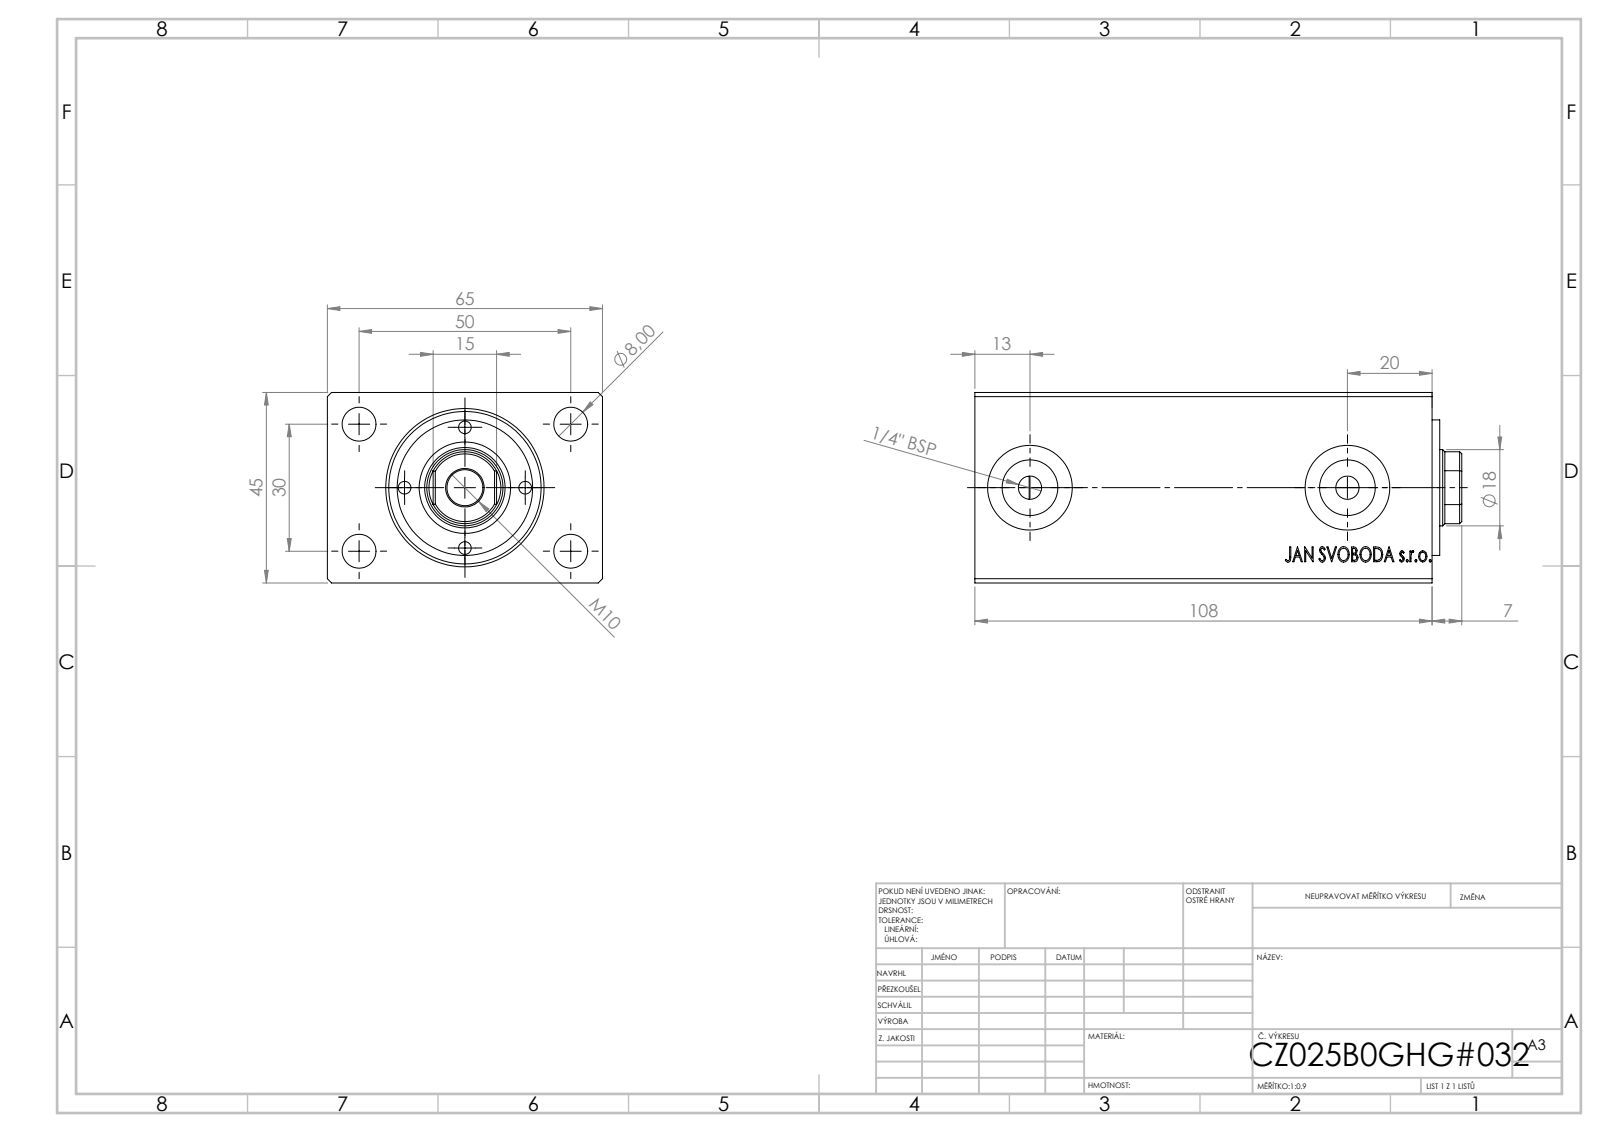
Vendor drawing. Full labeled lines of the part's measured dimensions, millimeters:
Part name (STEP PRODUCT): V500CZ; V500CZ_B_VC
STEP written by: SolidWorks 2019 (CONFIG_CONTROL_DESIGN)
Units: millimetres
Bodies: 3 solids, 873 faces (399 planar, 58 cylindrical, 416 other)
Overall size (bounding box): 115 × 65 × 45
Volume: 293 860 mm³ · Surface area: 54 520 mm²
Round holes (diameter × count): ⌀3 ×4, ⌀8 ×4, ⌀5.5 ×2, ⌀13.16 ×2, ⌀20 ×2, ⌀8.5 ×1, ⌀18 ×1, ⌀19 ×1, ⌀25 ×1, ⌀36 ×1
Round bosses / shafts (diameter × count): ⌀32 ×1
Partial cylindrical surfaces — rounded edges, fillets, slot ends (radius × count): R8.5 ×1
Main face-to-face distances: 45, 65, 108, 7, 107.8, 95.2, 12.6, 12.8, 1.8, 5.2
Hole centre spacings: 14.25, 18.45, 20.15, 25.01, 29.15, 38.48, 42.02, 28.5
